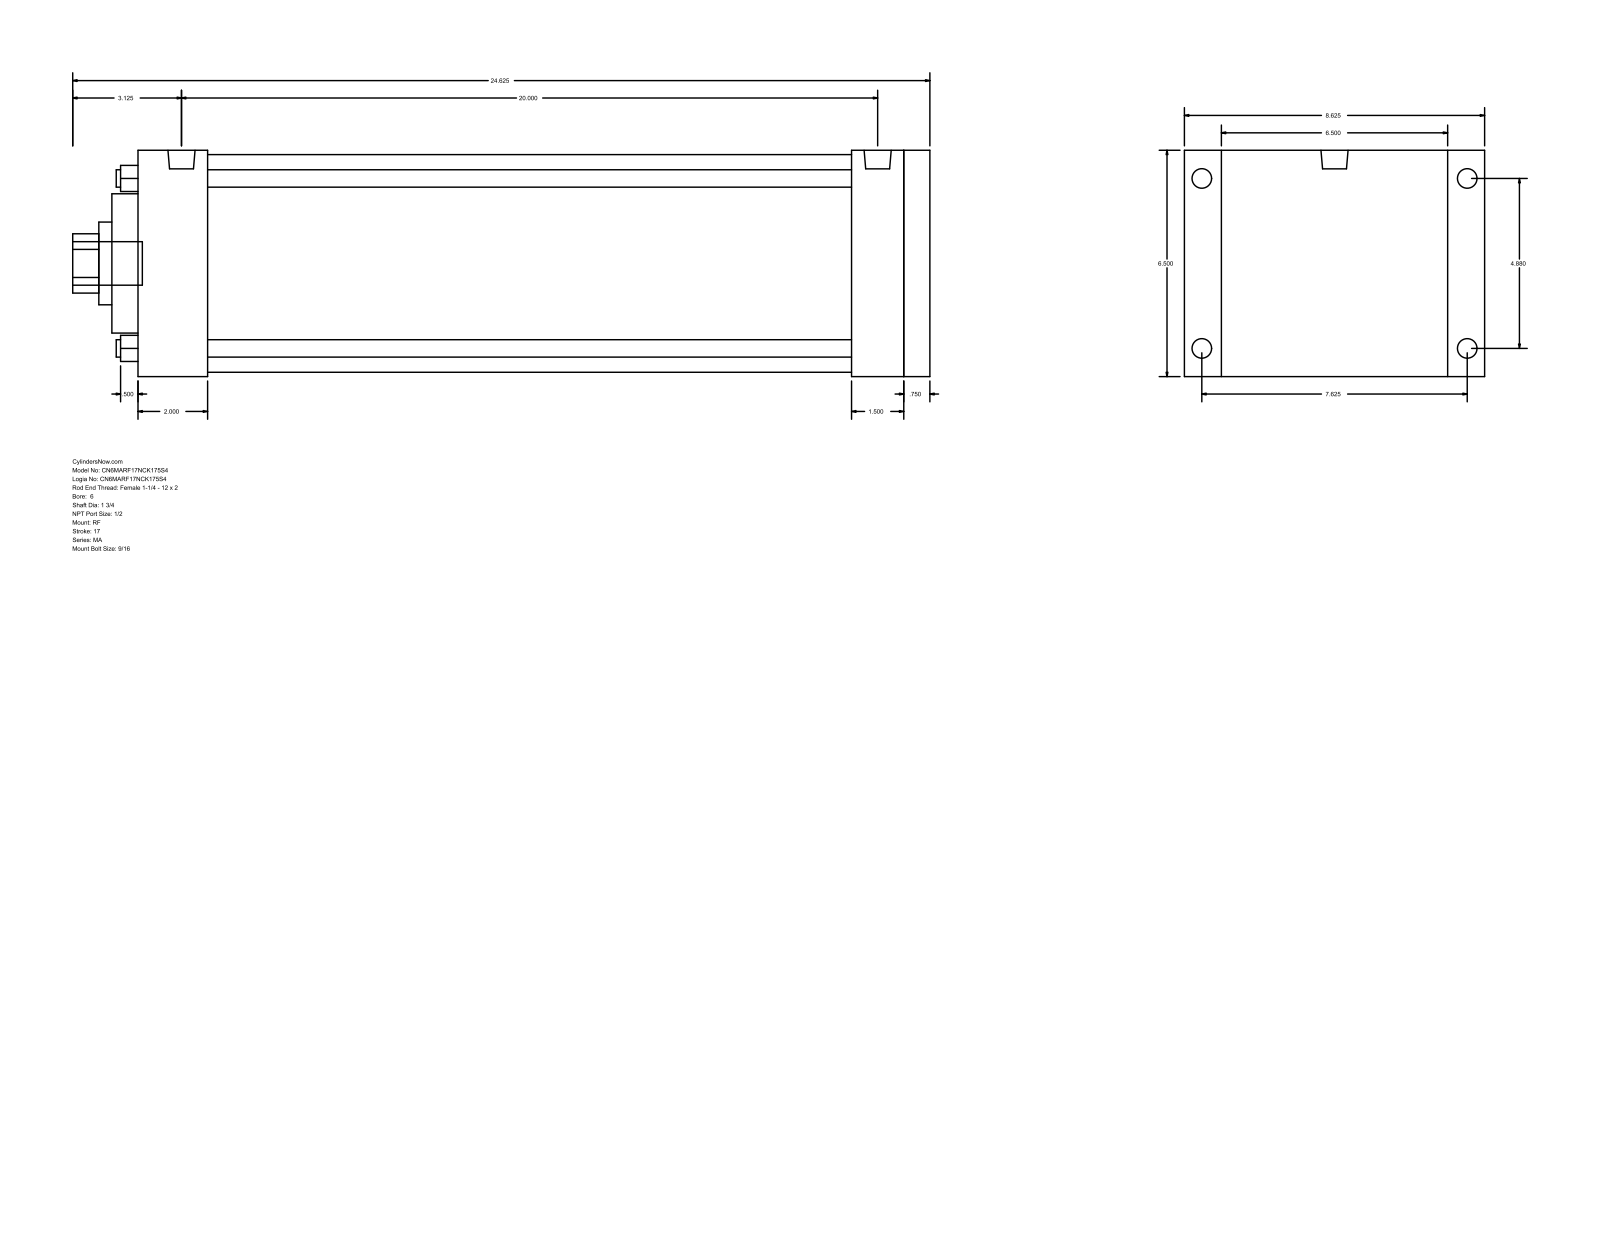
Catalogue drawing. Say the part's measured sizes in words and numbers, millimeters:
The part is named "MA_RF__0600_1.75". Its 3-D file was written by "GSSL Pune (CONFIG_CONTROL_DESIGN)". It is 0 solids with 94 faces: 65 planar, 29 cylindrical and 0 other. Overall it measures 625.48 by 219.07 by 165.1 millimeters. Round holes: 4 of diameter 12.7, 1 of diameter 44.45, 1 of diameter 60.33, 1 of diameter 101.6, 1 of diameter 158.75. Round bosses or shafts: 4 of diameter 17.46, 4 of diameter 14.29, 2 of diameter 19.77, 1 of diameter 31.75. Partial cylindrical surfaces (rounded edges, fillets, slot ends): 1 of radius 21.63. The main face-to-face distances are 165.1, 577.86, 558.8, 19.06, 19.05, 50.8, 508, 527.06, 520.71, 469.91. The hole center spacings are 87.65, 123.96, 175.31.
